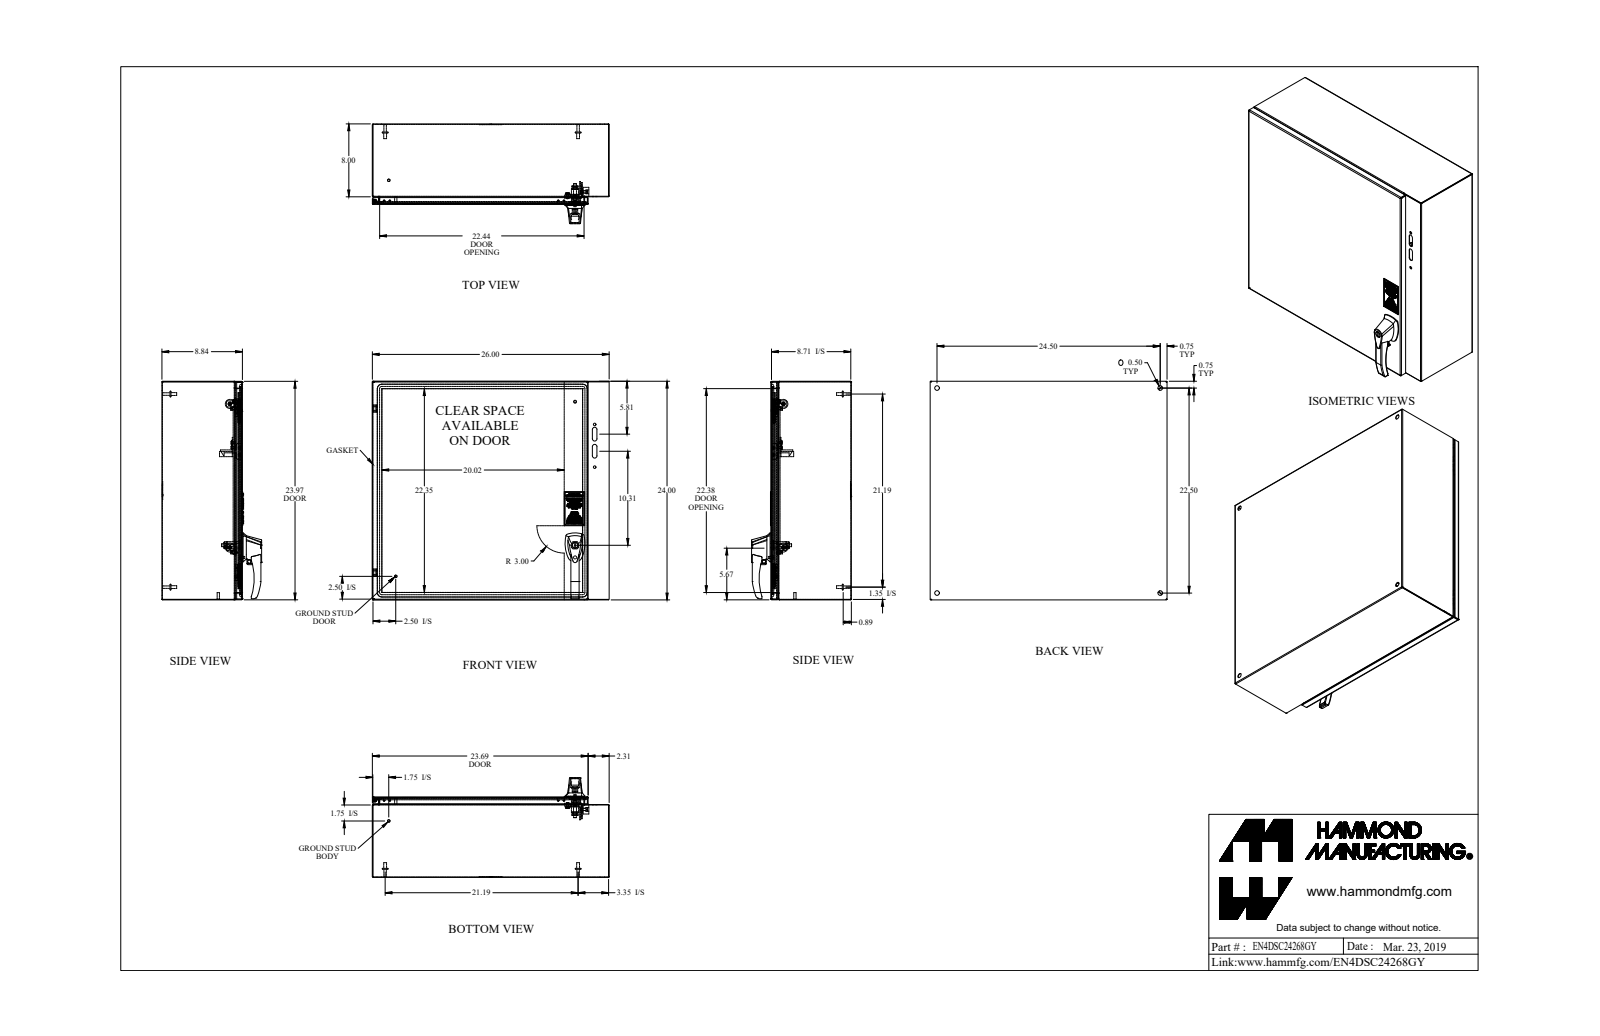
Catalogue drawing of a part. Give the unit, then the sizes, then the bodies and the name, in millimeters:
Units: millimetres
Overall size (bounding box): 660.4 × 609.6 × 278.2
Round holes (diameter × count): ⌀4.5 ×4, ⌀12.7 ×4, ⌀4 ×2, ⌀4.4 ×2, ⌀5.5 ×2, ⌀6.4 ×2, ⌀6.7 ×2, ⌀7.1 ×2, ⌀10.5 ×2, ⌀4.4 ×1, ⌀5 ×1, ⌀5.9 ×1
Round bosses / shafts (diameter × count): ⌀6.4 ×7, ⌀9.5 ×4, ⌀8 ×4, ⌀6.9 ×4, ⌀4 ×4, ⌀25.4 ×2, ⌀15.9 ×2, ⌀15.9 ×2
Partial cylindrical surfaces — rounded edges, fillets, slot ends (radius × count): R0.7 ×17, R2.2 ×17, R0.8 ×14, R6.4 ×14, R1.1 ×12, R2.1 ×12, R3.2 ×11, R1.5 ×6
Main face-to-face distances: 1.4, 1.8, 221.2, 222.6, 223, 224.5, 608.2, 659, 201.8, 606.7
Hole centre spacings: 400.1, 28.2, 571.5, 622.3, 844.9, 13.2, 19.1, 20.8
Volume: 2 689 000 mm³ · Surface area: 3 211 000 mm²
Bodies: 47 solids, 1047 faces (610 planar, 306 cylindrical, 131 other)
Part name (STEP PRODUCT): EN4DSC24268GY
STEP written by: SolidWorks 2019 (AUTOMOTIVE_DESIGN)
